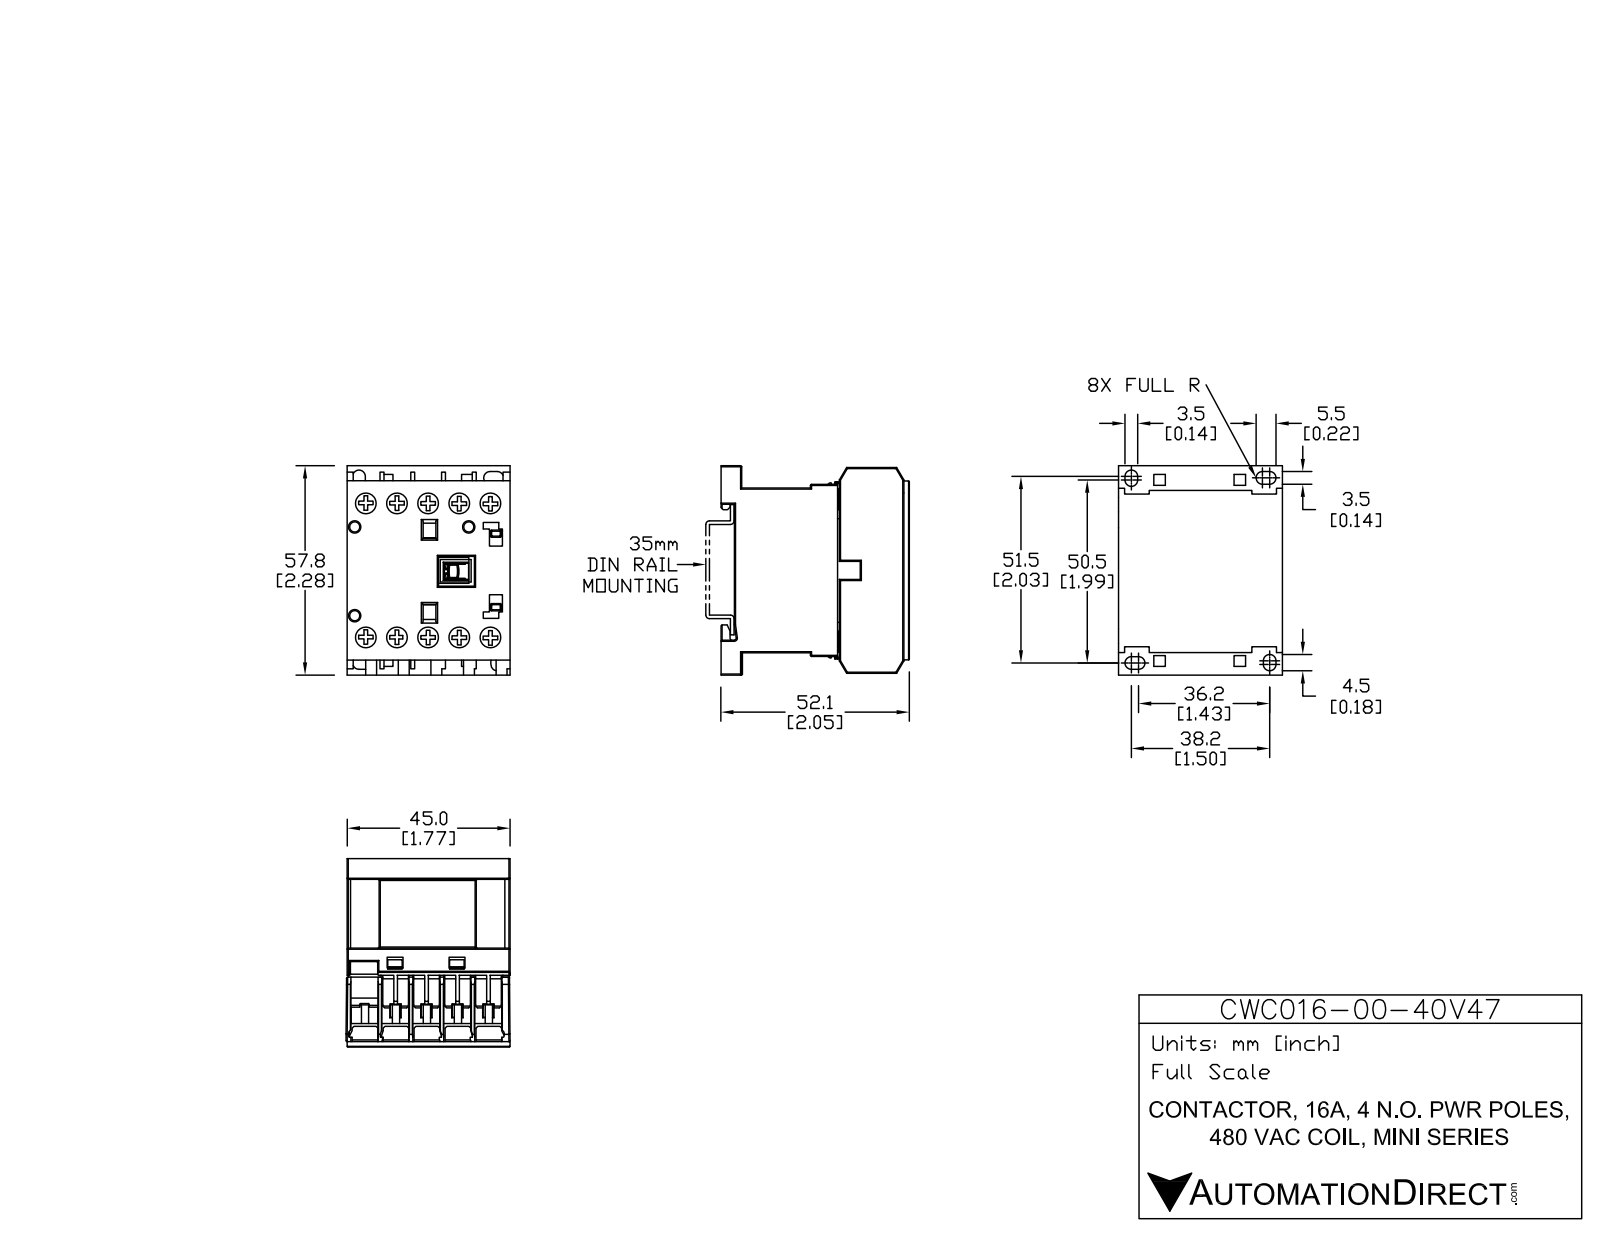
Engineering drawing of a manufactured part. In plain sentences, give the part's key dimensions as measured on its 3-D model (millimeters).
The part is named "CWC16-00-40V47". Its 3-D file was written by "SolidWorks 2013 (AUTOMOTIVE_DESIGN)". It is 15 solids with 535 faces: 445 planar, 90 cylindrical and 0 other. Overall it measures 58.04 by 52.12 by 45.75 millimeters. Its volume is 97 133 cubic millimeters and its surface area 30 437 square millimeters. Round holes: 10 of diameter 6.2, 3 of diameter 2.8. Round bosses or shafts: 10 of diameter 5.9. Partial cylindrical surfaces (rounded edges, fillets, slot ends): 20 of radius 0.3, 6 of radius 1.72, 2 of radius 1.73, 1 of radius 0.32, 1 of radius 0.42, 1 of radius 0.55. The main face-to-face distances are 8.25, 45.5, 1.25, 16.5, 9.5, 5.5, 17.75, 5.13, 10.63, 7. The hole center spacings are 8.55, 37.94, 17.1, 40.72, 36.96, 25.65, 44.99, 6.91.
